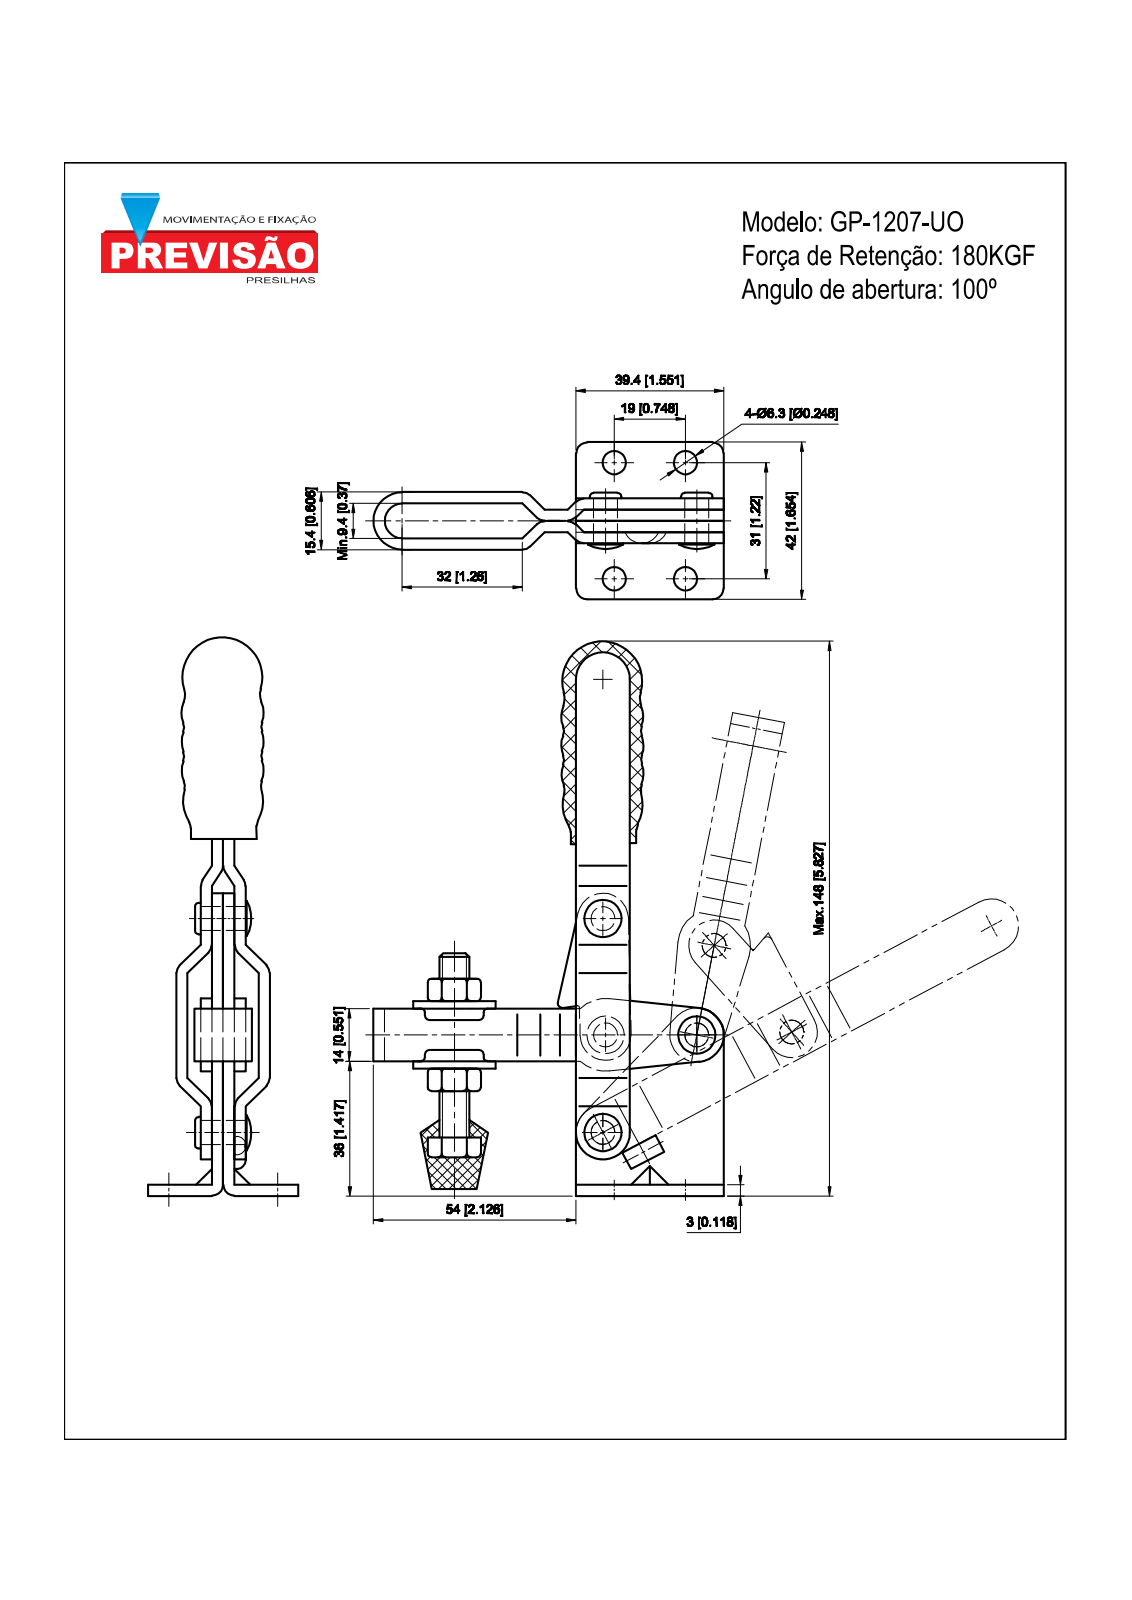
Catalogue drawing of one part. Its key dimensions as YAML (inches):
part_name: "CH-101-D-06.STEP; CH-101-D-04 CONNECTING-PLATE.STEP; CH-FC-56212 Nut.STEP; CH-101-D-03 STRAIGHT HANDLE.STEP (+7 more)"
step_written_by: "SolidWorks 2019 (AUTOMOTIVE_DESIGN)"
units: inches
bodies: {solids: 18, faces: 853, planar: 310, cylindrical: 257, other: 286}
overall_size: [5.876, 3.678, 1.654]
volume: 3.884
surface_area: 76.26
round_holes:
  - {diameter: 0.248, count: 6}
  - {diameter: 0.228, count: 4}
  - {diameter: 0.252, count: 4}
  - {diameter: 0.251, count: 2}
  - {diameter: 0.319, count: 2}
  - {diameter: 0.091, count: 1}
  - {diameter: 0.312, count: 1}
round_bosses_or_shafts:
  - {diameter: 0.821, count: 1}
  - {diameter: 0.312, count: 1}
  - {diameter: 0.081, count: 1}
partial_cylinders:
  - {radius: 0.118, count: 16}
  - {radius: 0.039, count: 10}
  - {radius: 0.118, count: 8}
  - {radius: 0.079, count: 4}
  - {radius: 0.118, count: 4}
  - {radius: 0.283, count: 3}
  - {radius: 0.185, count: 2}
  - {radius: 0.268, count: 2}
face_to_face_distances: [0.118, 0.236, 0.119, 0.237, 0.118, 0.354, 0.256, 0.374, 0.492, 0.61]
hole_center_spacings: [1.22, 0.748, 1.431, 0.949, 1.027, 1.42, 1.606, 1.975]
